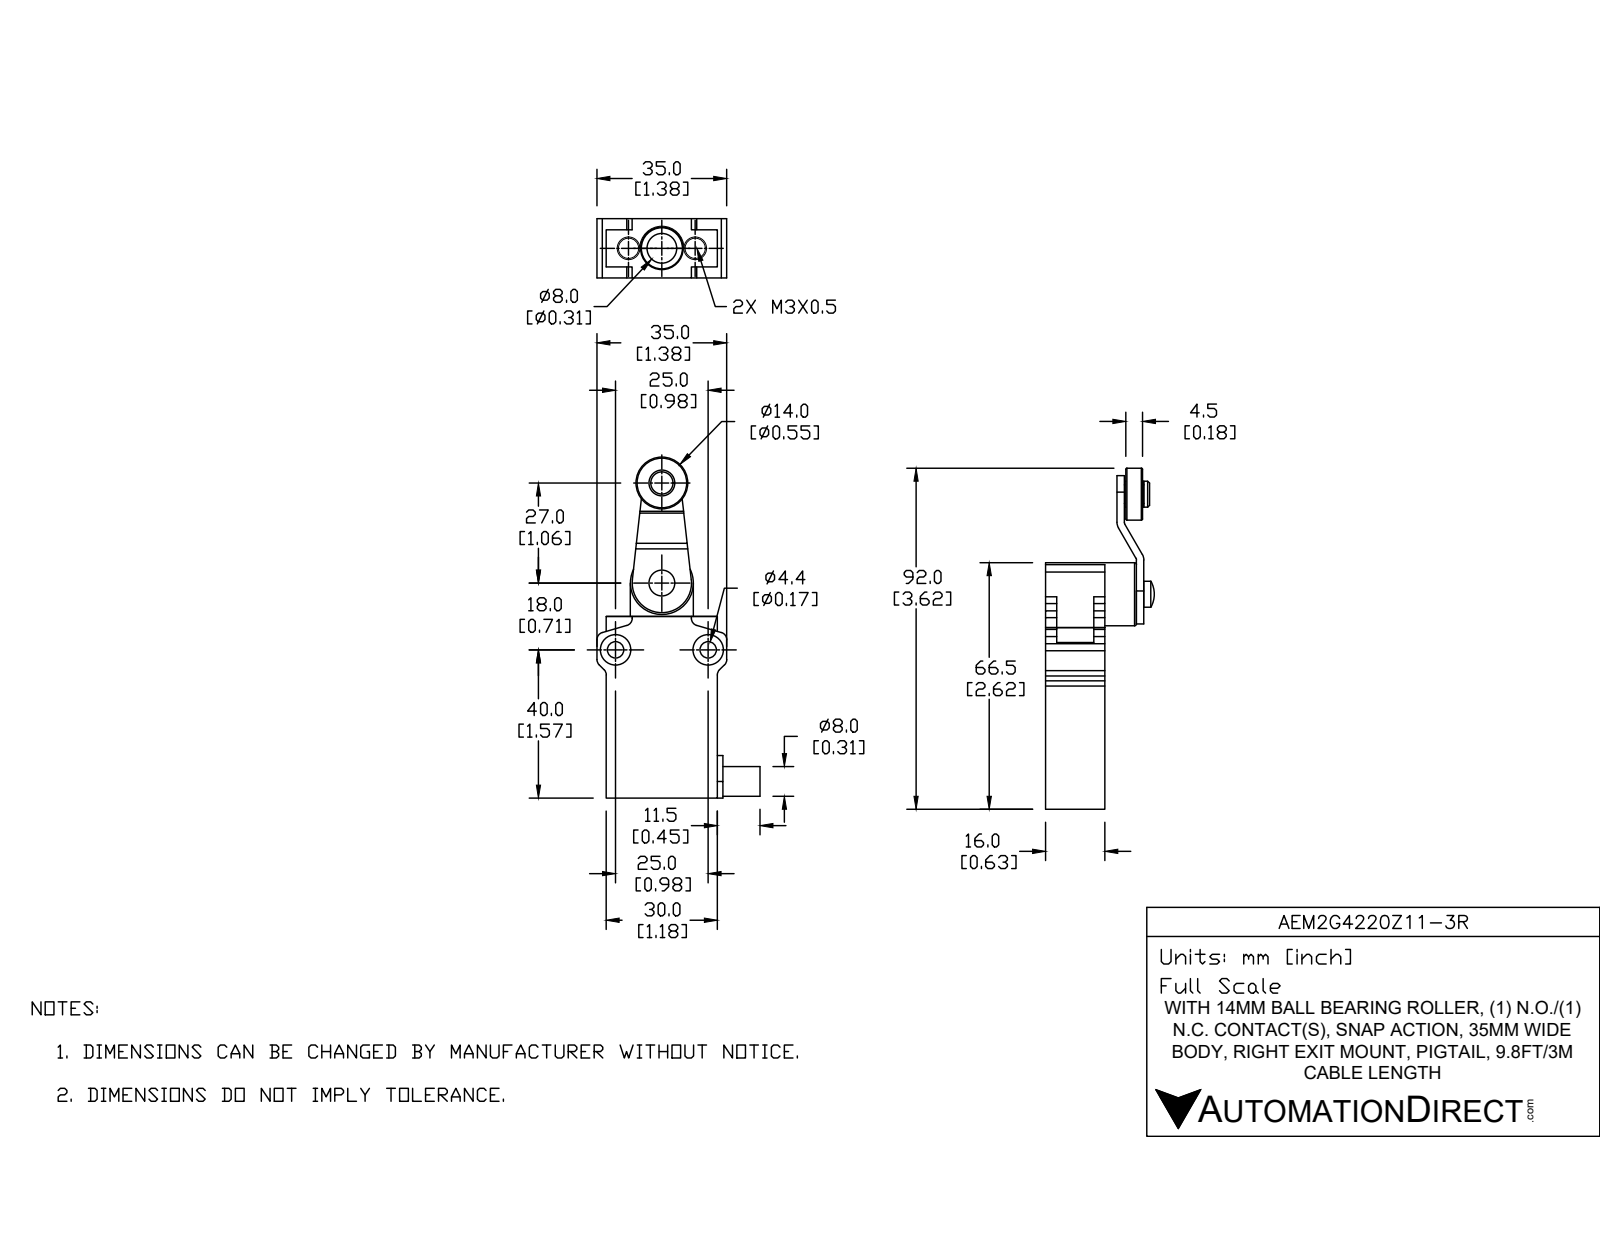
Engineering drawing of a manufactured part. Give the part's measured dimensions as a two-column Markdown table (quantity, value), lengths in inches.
| quantity | value |
| --- | --- |
| part name | AEM2G4320Z11-3R |
| STEP written by | SolidWorks 2017 (AUTOMOTIVE_DESIGN) |
| units | inches |
| bodies | 7 solids, 543 faces (297 planar, 73 cylindrical, 173 other) |
| overall size | 3.602 × 1.87 × 1.26 |
| volume | 1.855 in³ |
| surface area | 17.74 in² |
| round holes (diameter × count) | 0.118 × 2, 0.173 × 2, 0.323 × 2, 0.098 × 1, 0.138 × 1, 0.161 × 1, 0.197 × 1, 0.224 × 1 |
| round bosses / shafts (diameter × count) | 0.276 × 2, 0.622 × 1, 0.551 × 1, 0.394 × 1, 0.323 × 1, 0.236 × 1, 0.197 × 1, 0.157 × 1 |
| partial cylindrical surfaces (radius × count) | 0.079 × 8, 0.039 × 2, 0.118 × 2, 0.256 × 1, 0.315 × 1 |
| main face-to-face distances | 0.63, 1.181, 1.929, 0.354, 0.079, 0.984, 0.28, 0.902, 0.102, 0.472 |
| hole center spacings | 0.863, 1.82, 0.748, 0.984, 1.043 |
